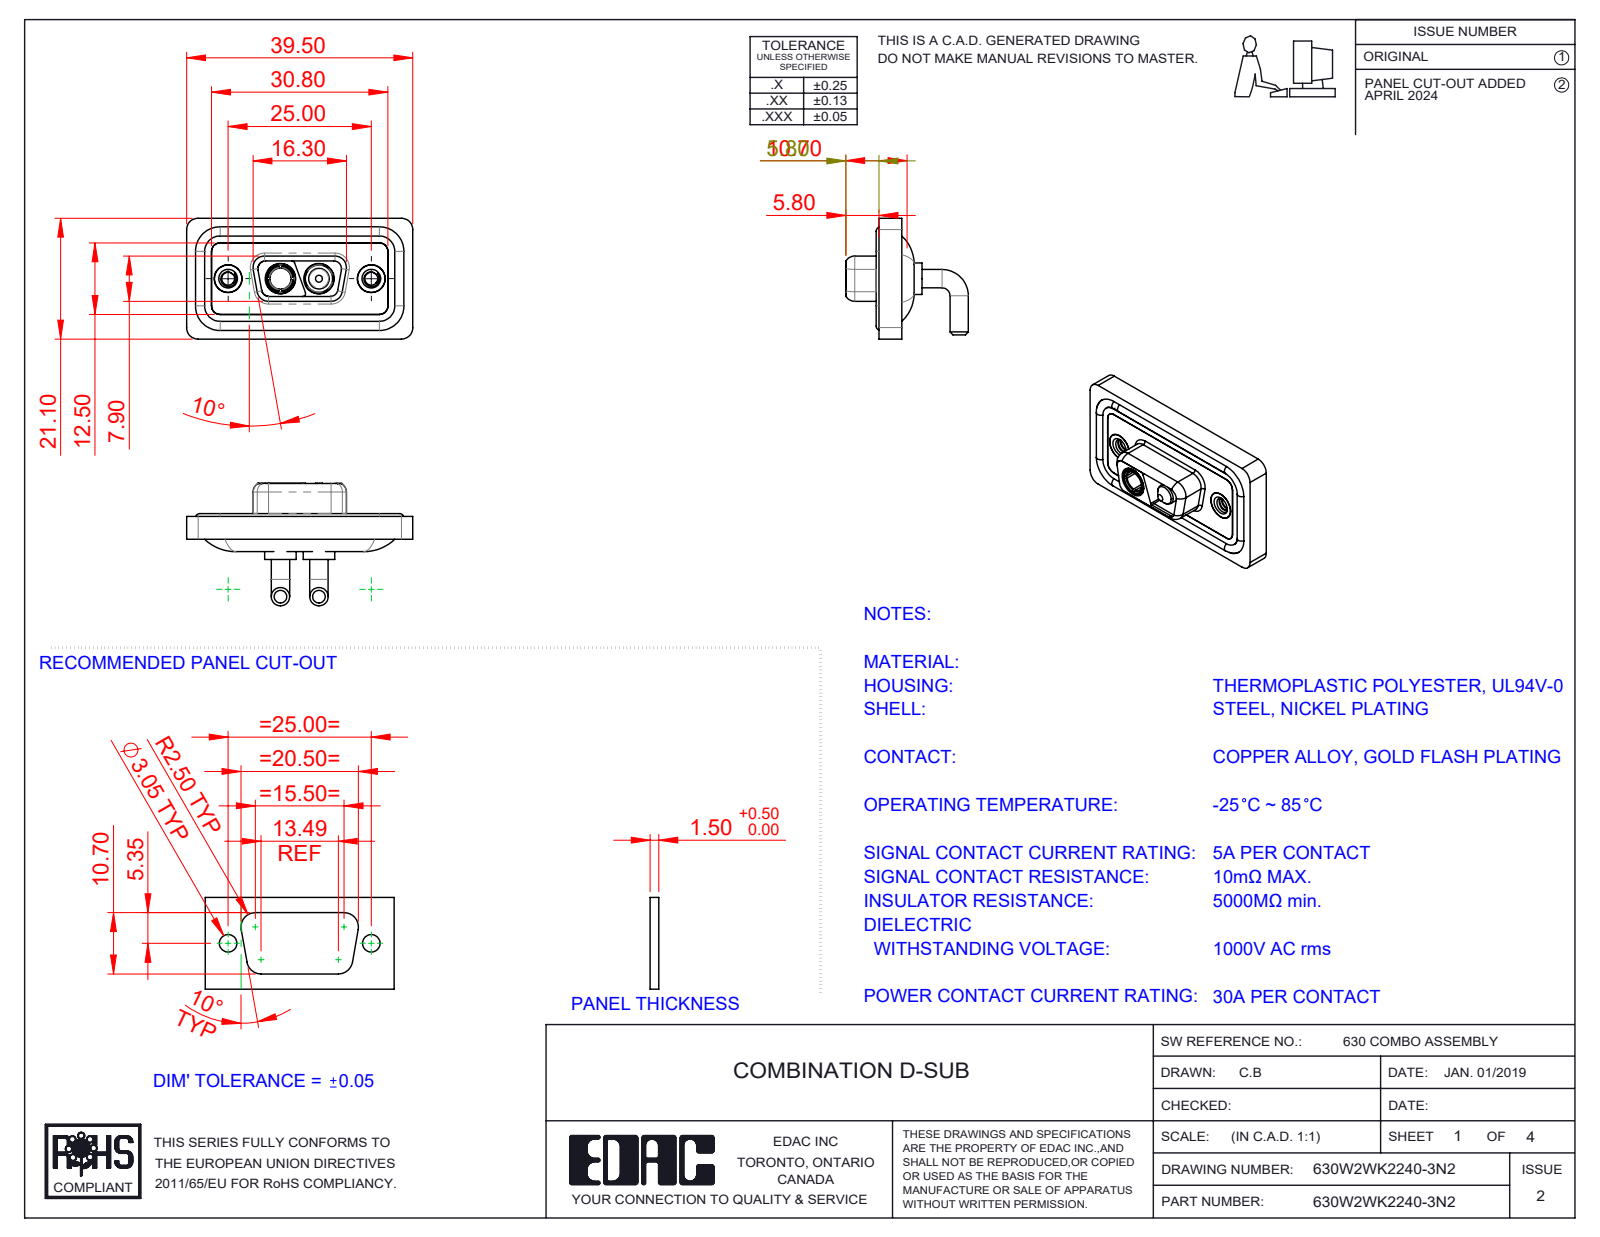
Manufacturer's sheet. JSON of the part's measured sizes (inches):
{"part_name": "630Combo Threaded Rivet_2; 630Combo Shell Rear_09 Contacts; 630Combo Housing_2WK2; Power Socket_30A RA (+4 more)", "step_written_by": "SolidWorks 2023 (CONFIG_CONTROL_DESIGN)", "units": "inches", "bodies": {"solids": 11, "faces": 508, "planar": 144, "cylindrical": 235, "other": 129}, "overall_size": [1.555, 0.843, 0.831], "volume_in3": 0.291, "surface_area_in2": 11.67, "round_holes": [[0.191, 4], [0.089, 2], [0.157, 2], [0.159, 2], [0.197, 2], [0.209, 2], [0.146, 1]], "round_bosses_or_shafts": [[0.126, 4], [0.063, 4], [0.217, 2], [0.205, 2], [0.195, 2], [0.189, 2], [0.187, 2], [0.148, 2]], "partial_cylinders_radius": [[0.059, 18], [0.079, 18], [0.053, 8], [0.063, 8], [0.02, 6], [0.01, 4], [0.024, 4], [0.026, 4]], "face_to_face_distances": [0.016, 0.043, 0.114, 0.071, 0.098, 0.063, 0.122, 0.059, 0.083, 0.146], "hole_center_spacings": [0.36, 0.624, 0.265, 0.984]}
